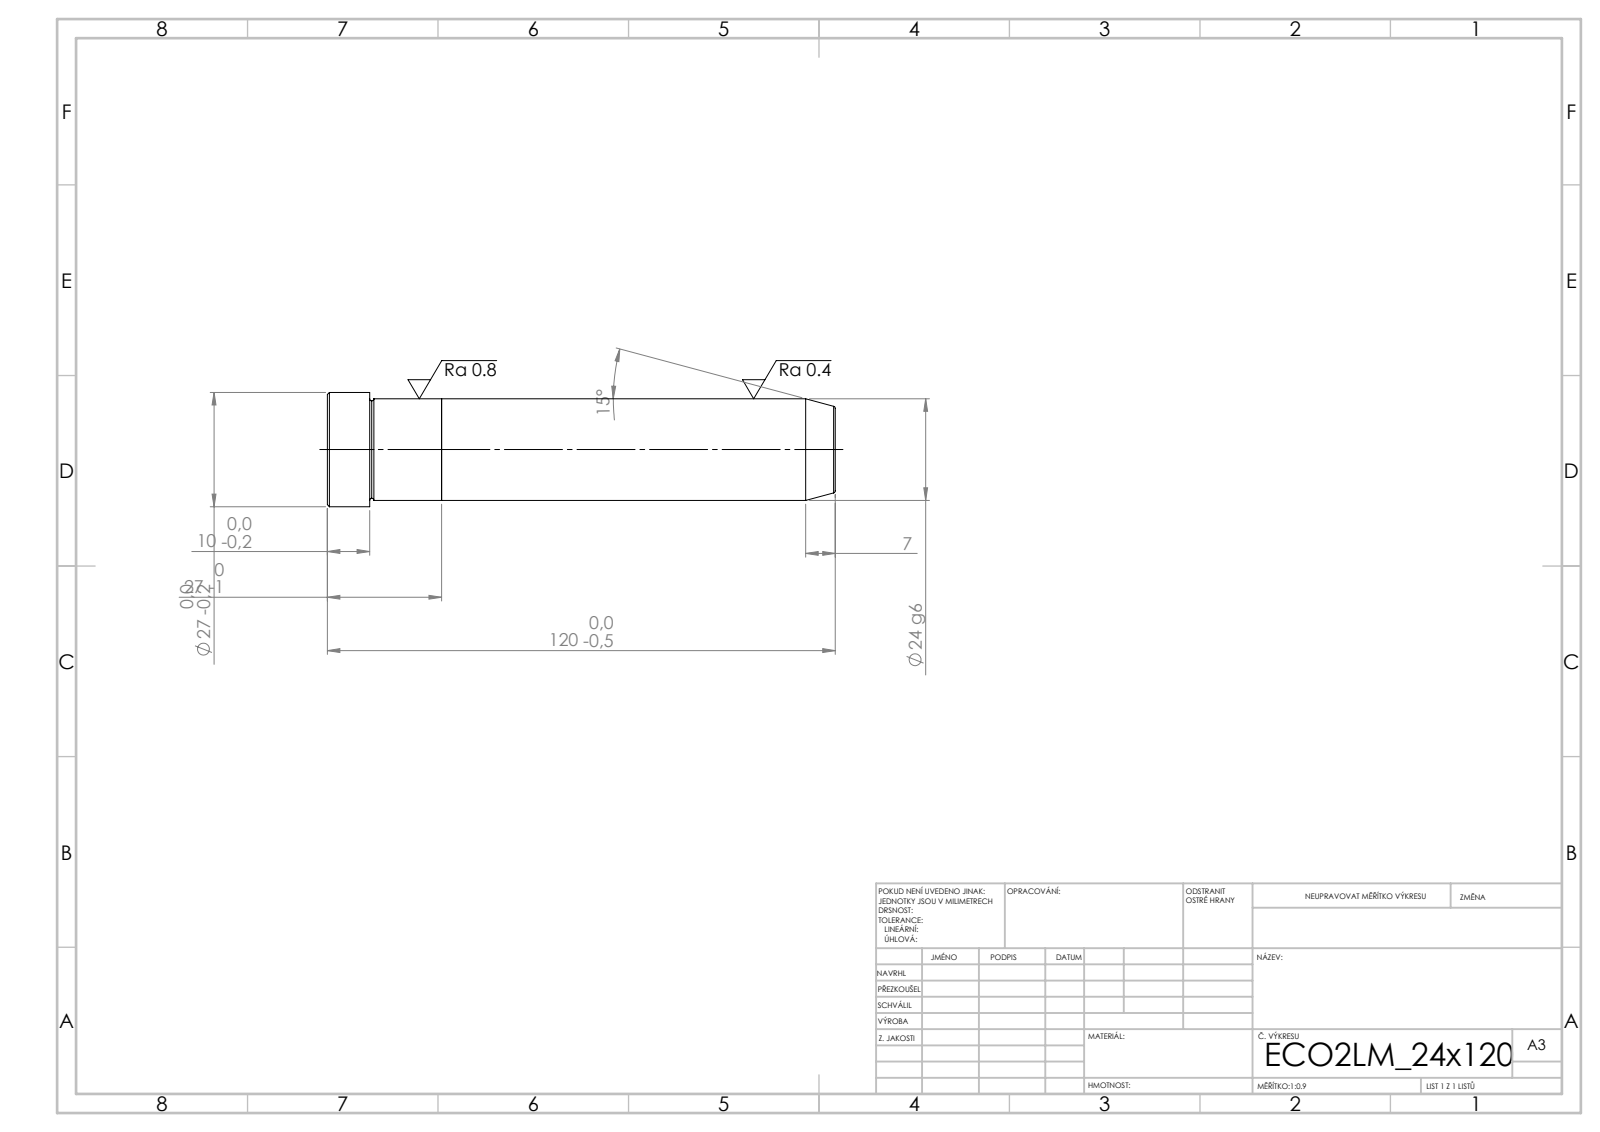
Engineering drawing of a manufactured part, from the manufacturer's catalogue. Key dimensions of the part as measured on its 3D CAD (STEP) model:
STEP written by: SolidWorks 2019 (CONFIG_CONTROL_DESIGN)
Units: millimetres
Bodies: 2 solids, 21 faces (5 planar, 6 cylindrical, 10 other)
Overall size (bounding box): 120 × 27 × 27
Volume: 54 978 mm³ · Surface area: 11 045 mm²
Round bosses / shafts (diameter × count): ⌀27 ×1, ⌀24 ×1
Main face-to-face distances: 27, 93, 120, 110, 17, 10
